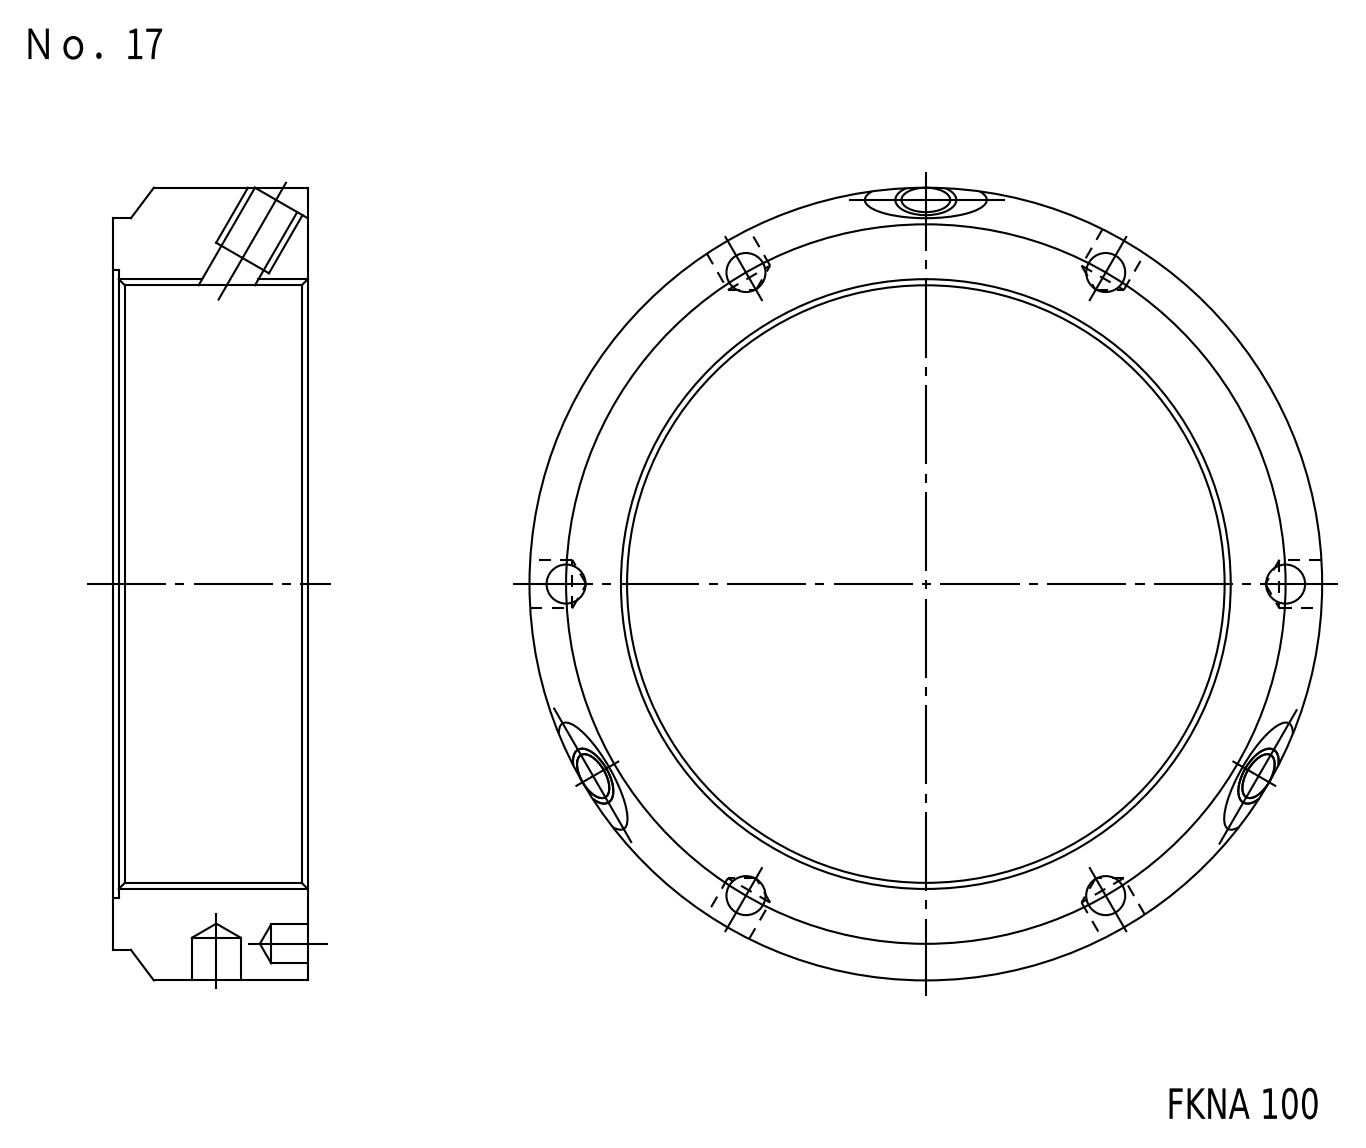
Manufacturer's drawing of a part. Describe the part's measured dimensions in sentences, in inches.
The part is named "FKD FKNA100". Its 3-D file was written by "Autodesk Inventor LT (CONFIG_CONTROL_DESIGN)". It is 1 solid with 44 faces: 6 planar, 25 cylindrical and 13 other. Overall it measures 5.118 by 5.118 by 1.26 inches. Its volume is 9.826 cubic inches and its surface area 54.74 square inches. Round holes: 6 of diameter 0.252, 3 of diameter 0.315, 3 of diameter 0.33, 3 of diameter 0.402, 1 of diameter 3.937, 1 of diameter 4.055. Round bosses or shafts: 1 of diameter 5.118, 1 of diameter 4.724. Partial cylindrical surfaces (rounded edges, fillets, slot ends): 3 of radius 0.787. The main face-to-face distances are 1.26, 0.059, 1.201. The hole center spacings are 2.323, 4.023, 4.024, 4.646, 4.646.
